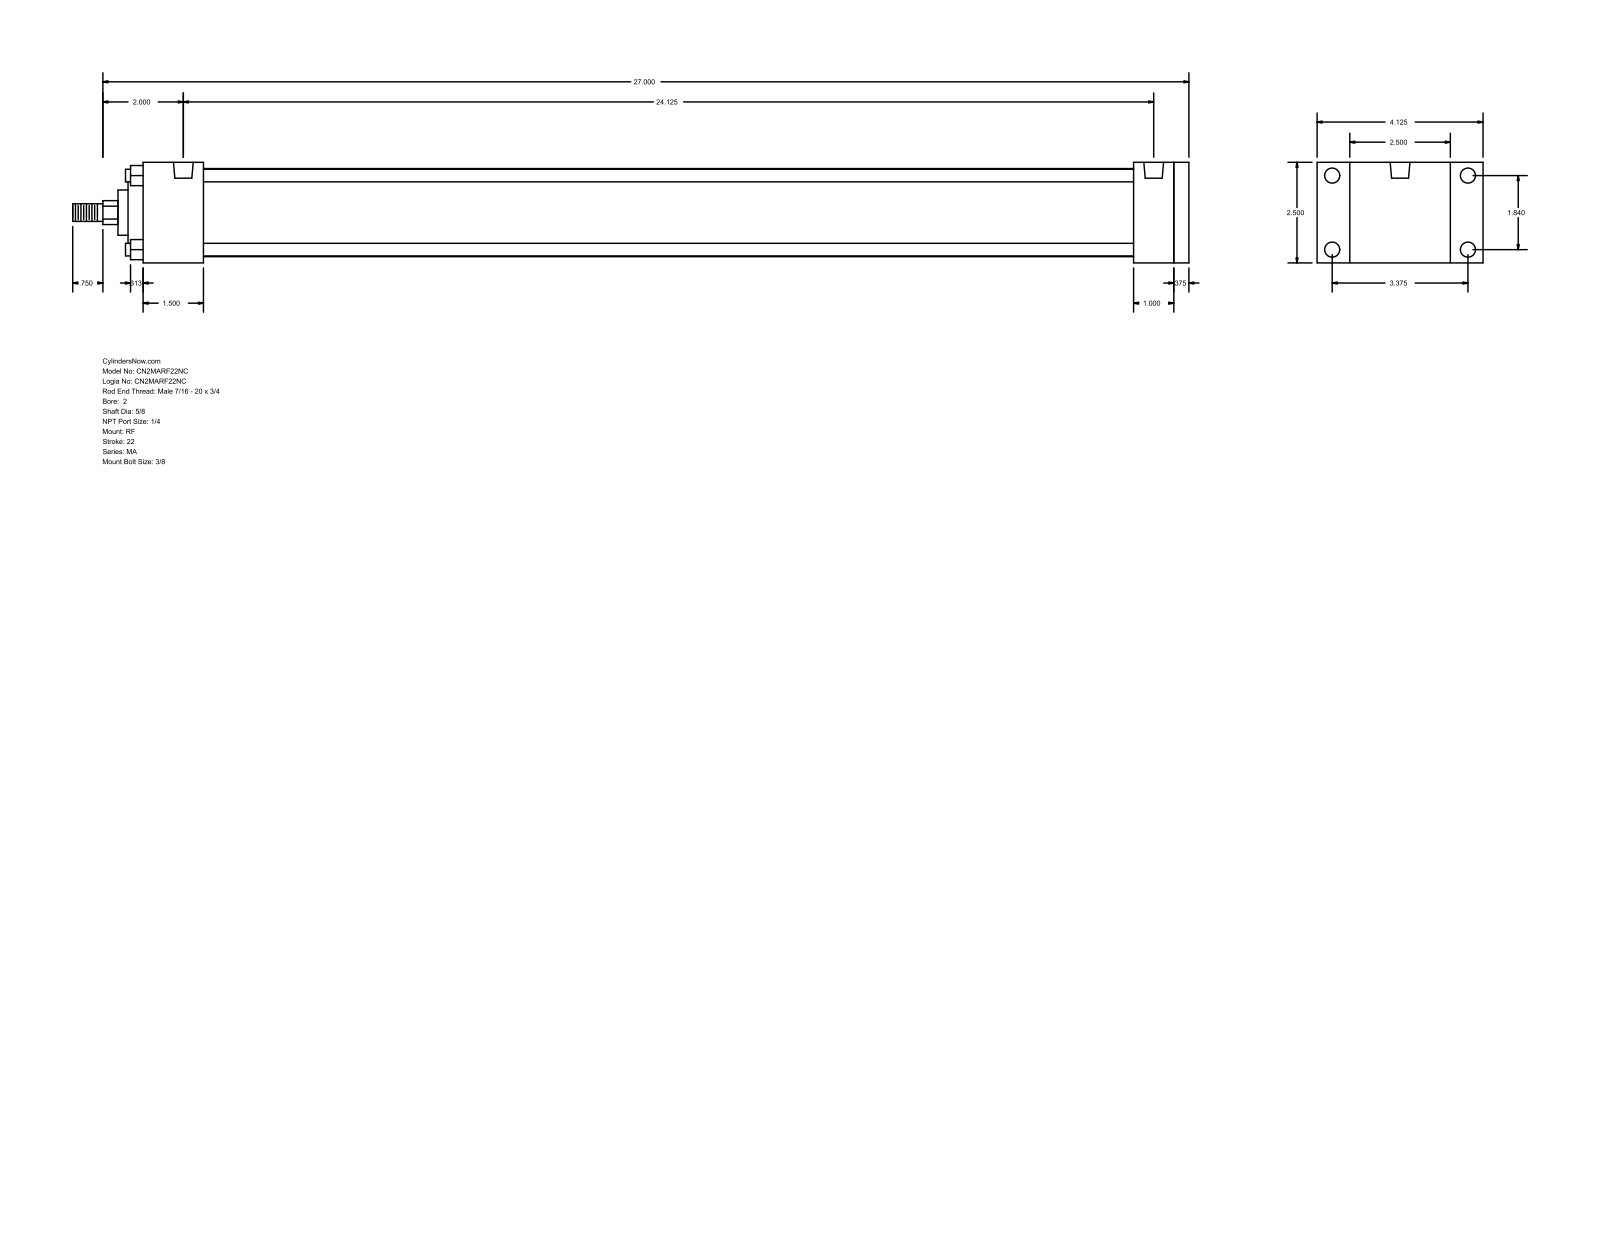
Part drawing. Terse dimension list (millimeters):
name: MA_RF__0200_0.625
written by: GSSL Pune (CONFIG_CONTROL_DESIGN)
unit: mm
bodies: 0 solids, 94 faces (65 planar, 29 cylindrical, 0 other)
size: 704.85 × 104.78 × 63.5
holes: 4× ⌀7.94, 4× ⌀9.53, 2× ⌀12.49
bosses: 4× ⌀7.94, 1× ⌀55.63, 1× ⌀50.8, 1× ⌀28.57, 1× ⌀15.88, 1× ⌀11.11
rounds: 1× R7.54
face distances: 63.5, 9.53, 38.1, 650.87, 660.4, 669.92, 612.77, 622.3, 625.48, 587.38
hole spacings: 46.74, 85.72, 97.63, 612.78
